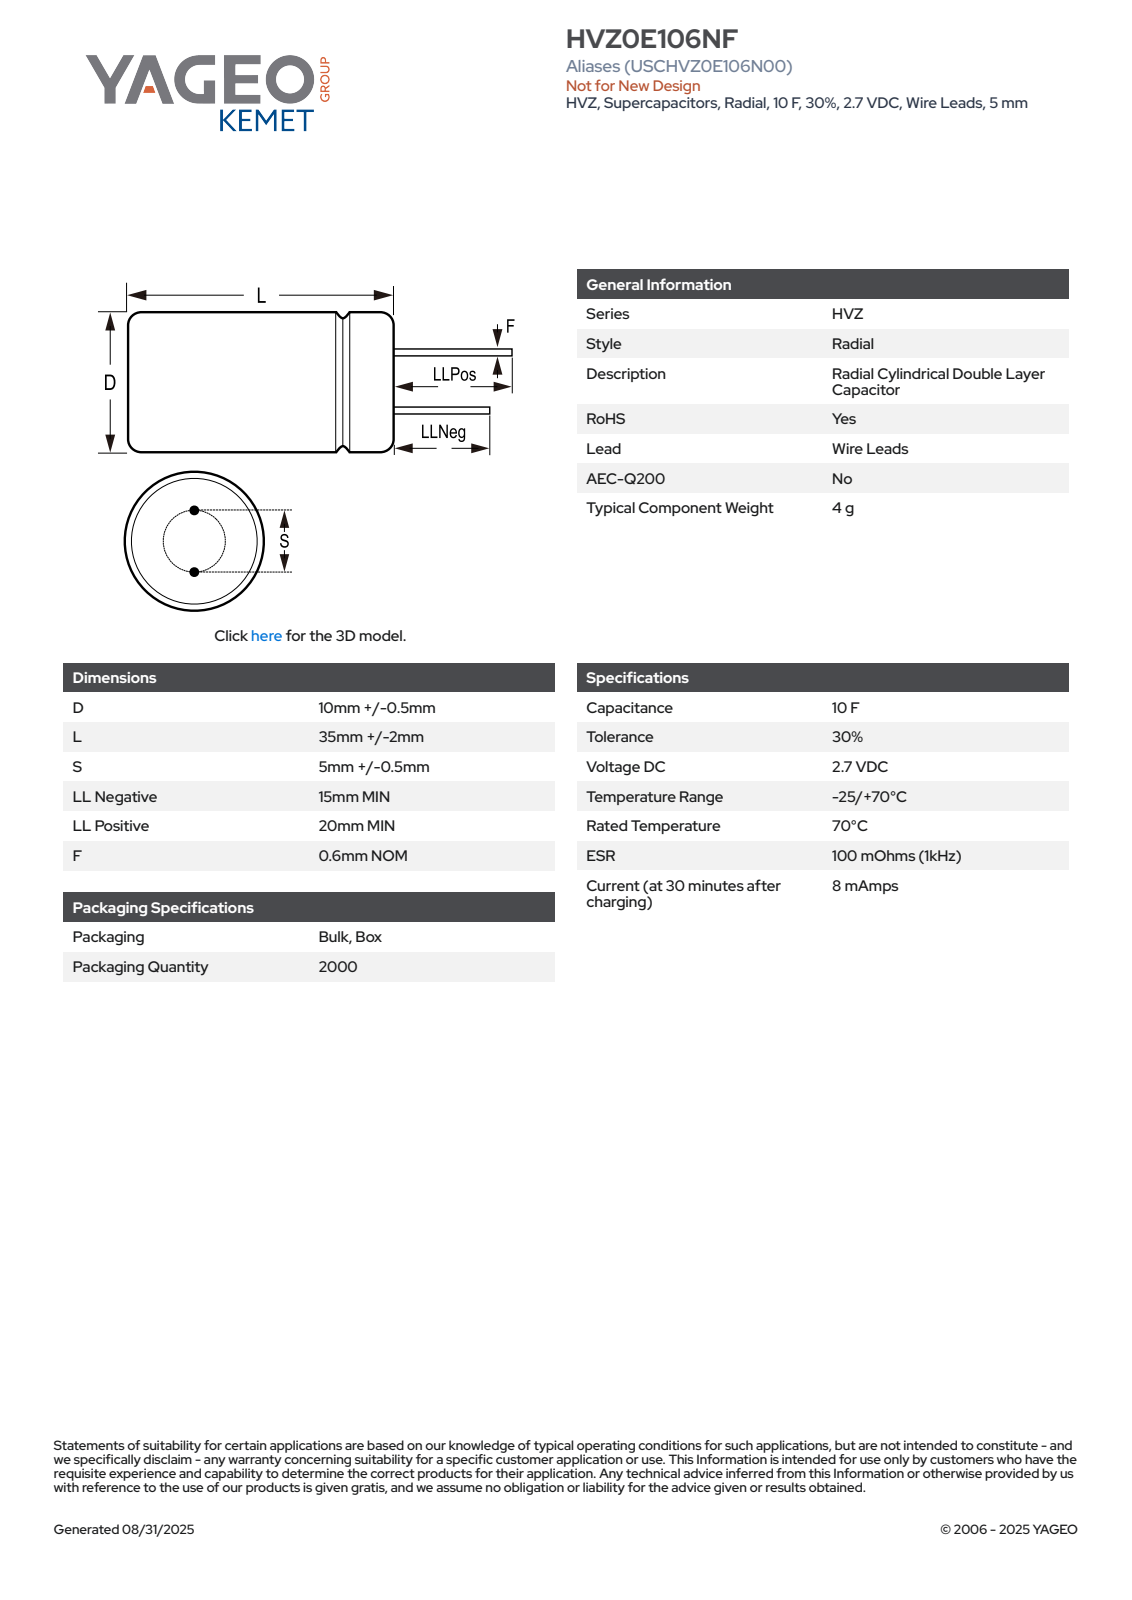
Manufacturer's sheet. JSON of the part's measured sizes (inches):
{"part_name": "CDR_CCW_D10.5L37S5F0.6", "step_written_by": "SolidWorks 2014 (AUTOMOTIVE_DESIGN)", "units": "inches", "bodies": {"solids": 1, "faces": 82, "planar": 26, "cylindrical": 17, "other": 39}, "overall_size": [2.244, 0.414, 0.413], "volume_in3": 0.195, "surface_area_in2": 2.232, "round_bosses_or_shafts": [[0.024, 2], [0.413, 1]], "partial_cylinders_radius": [[0.207, 1]], "face_to_face_distances": [1.457, 2.047, 2.244, 0.591, 0.787, 0.197]}
